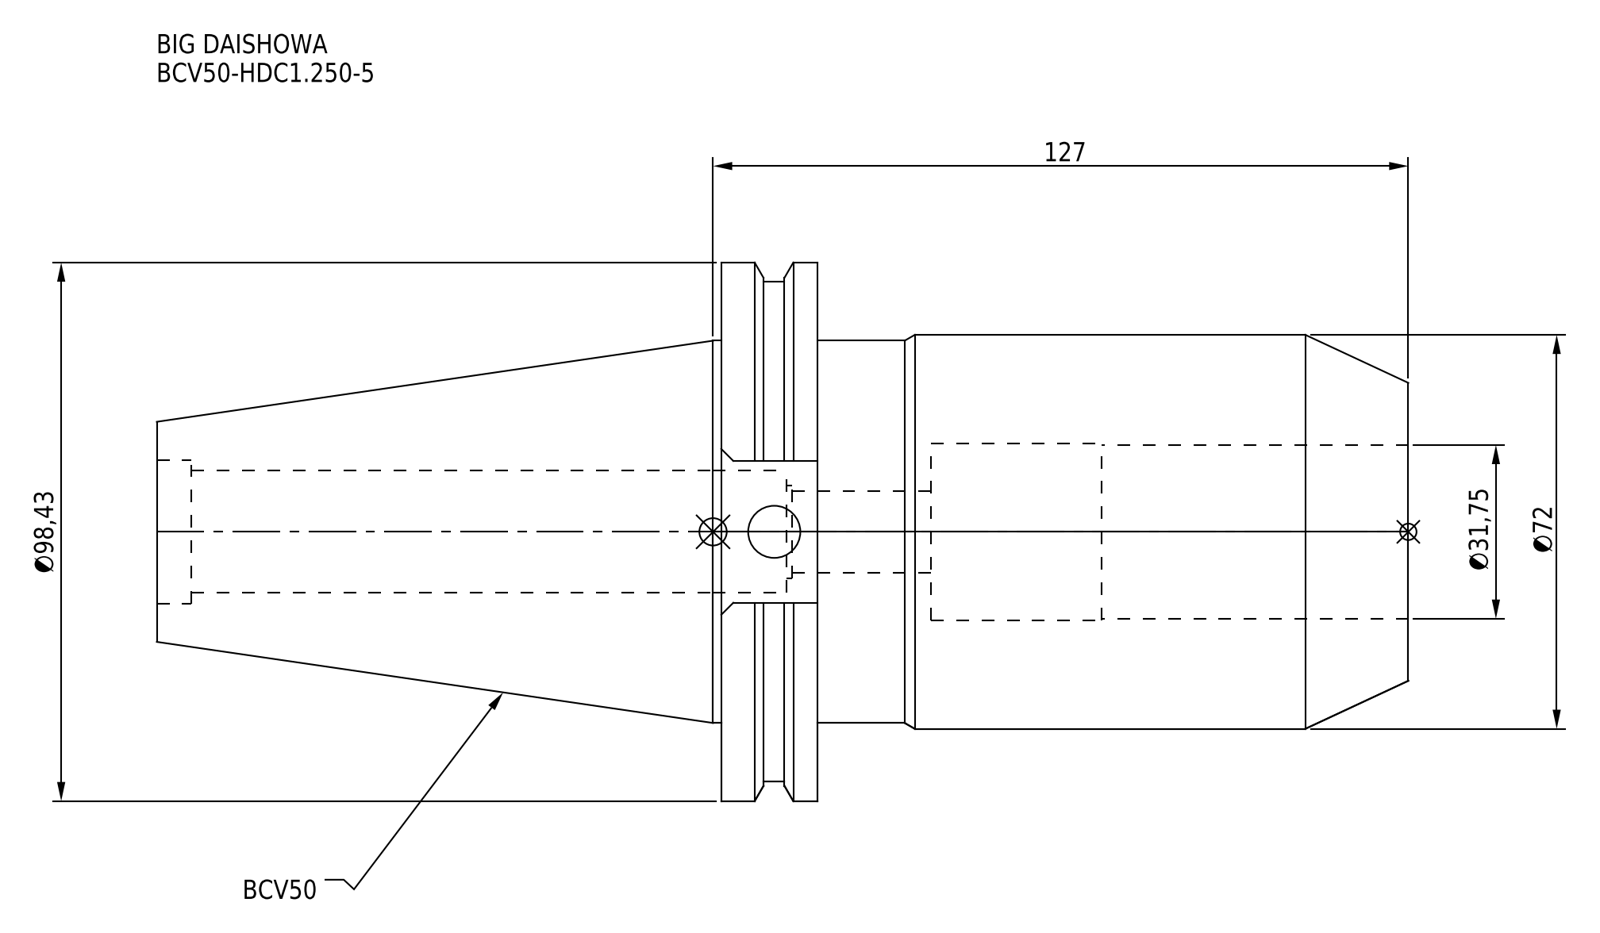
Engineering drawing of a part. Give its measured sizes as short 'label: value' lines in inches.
name: BCV50-HDC1_250-5
written by: CREO PARAMETRIC BY PTC INC, 2016380 (AUTOMOTIVE_DESIGN)
unit: in
bodies: 1 solid, 62 faces (24 planar, 28 cylindrical, 10 other)
size: 9 × 3.875 × 3.738
volume: 40.82 in³; area: 119.6 in²
holes: 1× ⌀0.375, 1× ⌀0.591, 1× ⌀0.669, 1× ⌀0.878, 1× ⌀1.033, 1× ⌀1.25, 1× ⌀1.272
bosses: 1× ⌀3.875, 1× ⌀3.594, 1× ⌀2.835, 1× ⌀2.75
face distances: 0.691, 4.25, 4.941, 9, 4.75, 4.059, 3.433, 0.817, 1.508, 5.567
